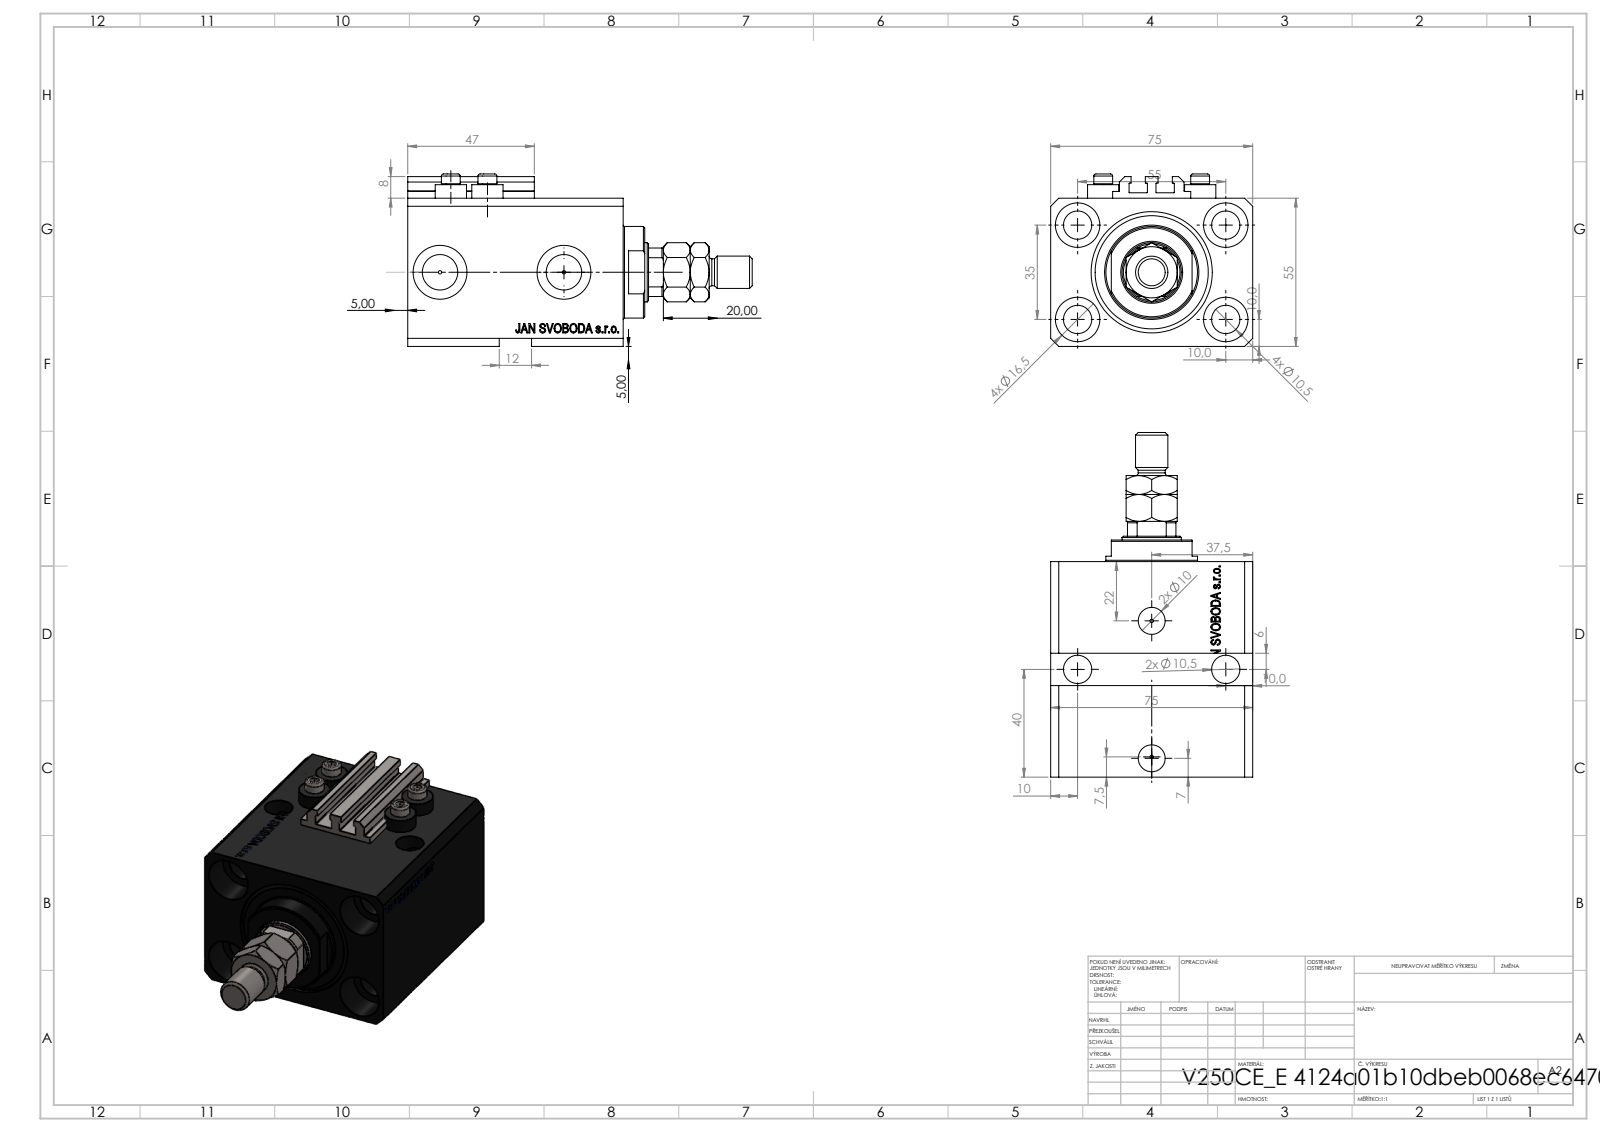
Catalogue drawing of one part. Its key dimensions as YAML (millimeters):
part_name: "V250CE_C_VCP; MTA; V250CE_E_Body; ALLEN BOLT V250CE (+1 more)"
step_written_by: "SolidWorks 2019 (CONFIG_CONTROL_DESIGN)"
units: millimeters
bodies: {solids: 8, faces: 247, planar: 101, cylindrical: 46, other: 100}
overall_size: [128, 59, 45]
volume: 80295
surface_area: 24472
round_holes:
  - {diameter: 10.5, count: 1}
  - {diameter: 22, count: 1}
round_bosses_or_shafts:
  - {diameter: 7, count: 4}
  - {diameter: 4, count: 4}
  - {diameter: 45, count: 1}
  - {diameter: 34, count: 1}
  - {diameter: 32, count: 1}
  - {diameter: 12, count: 1}
  - {diameter: 10, count: 1}
partial_cylinders:
  - {radius: 0.2, count: 10}
  - {radius: 10.5, count: 1}
face_to_face_distances: [2.5, 8, 15, 55.1, 2, 24, 30, 6, 5.5, 0.5]
